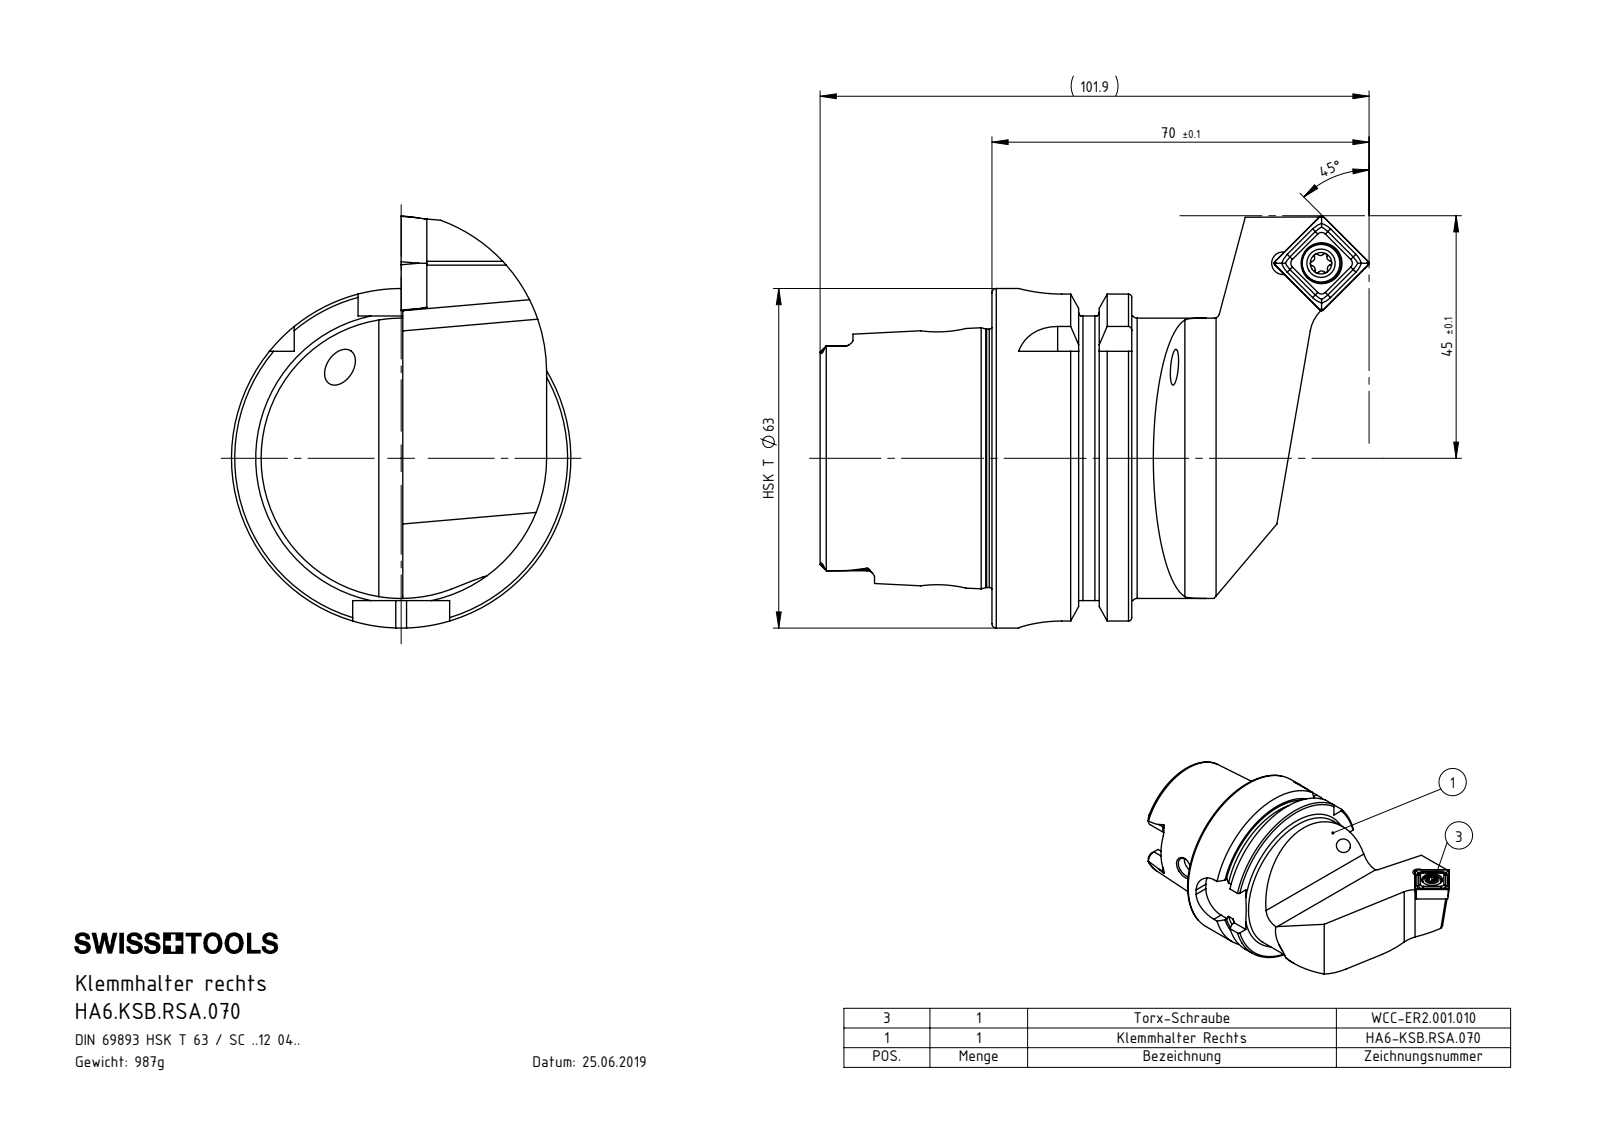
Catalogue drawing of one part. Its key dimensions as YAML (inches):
part_name: "HA6-KSB.RSA.070_A_Fertigbearbeitung; HA6.KSB.RSA.070; SCMT120404; WCC-ER2.001.010_A"
step_written_by: "SolidWorks 2017 (AUTOMOTIVE_DESIGN)"
units: inches
bodies: {solids: 3, faces: 288, planar: 78, cylindrical: 84, other: 126}
overall_size: [4.012, 3.012, 2.48]
volume: 7.675
surface_area: 45.45
round_holes:
  - {diameter: 0.165, count: 2}
  - {diameter: 0.197, count: 2}
  - {diameter: 0.217, count: 1}
  - {diameter: 0.236, count: 1}
  - {diameter: 0.295, count: 1}
  - {diameter: 0.299, count: 1}
  - {diameter: 0.331, count: 1}
  - {diameter: 0.394, count: 1}
  - {diameter: 0.669, count: 1}
  - {diameter: 0.748, count: 1}
  - {diameter: 1.339, count: 1}
  - {diameter: 1.575, count: 1}
round_bosses_or_shafts:
  - {diameter: 2.48, count: 1}
  - {diameter: 2.163, count: 1}
  - {diameter: 2.047, count: 1}
  - {diameter: 1.887, count: 1}
  - {diameter: 0.276, count: 1}
  - {diameter: 0.197, count: 1}
partial_cylinders:
  - {radius: 0.015, count: 6}
  - {radius: 0.055, count: 6}
  - {radius: 0.113, count: 4}
  - {radius: 0.315, count: 4}
  - {radius: 0.027, count: 3}
  - {radius: 0.027, count: 3}
  - {radius: 0.236, count: 1}
  - {radius: 0.276, count: 1}
face_to_face_distances: [1.022, 0.63, 0.392, 1.256, 1.648, 2.278, 2.079, 0.858, 0.467, 2.114]
hole_center_spacings: [0.278, 0.283, 2.336, 2.562, 2.565]
